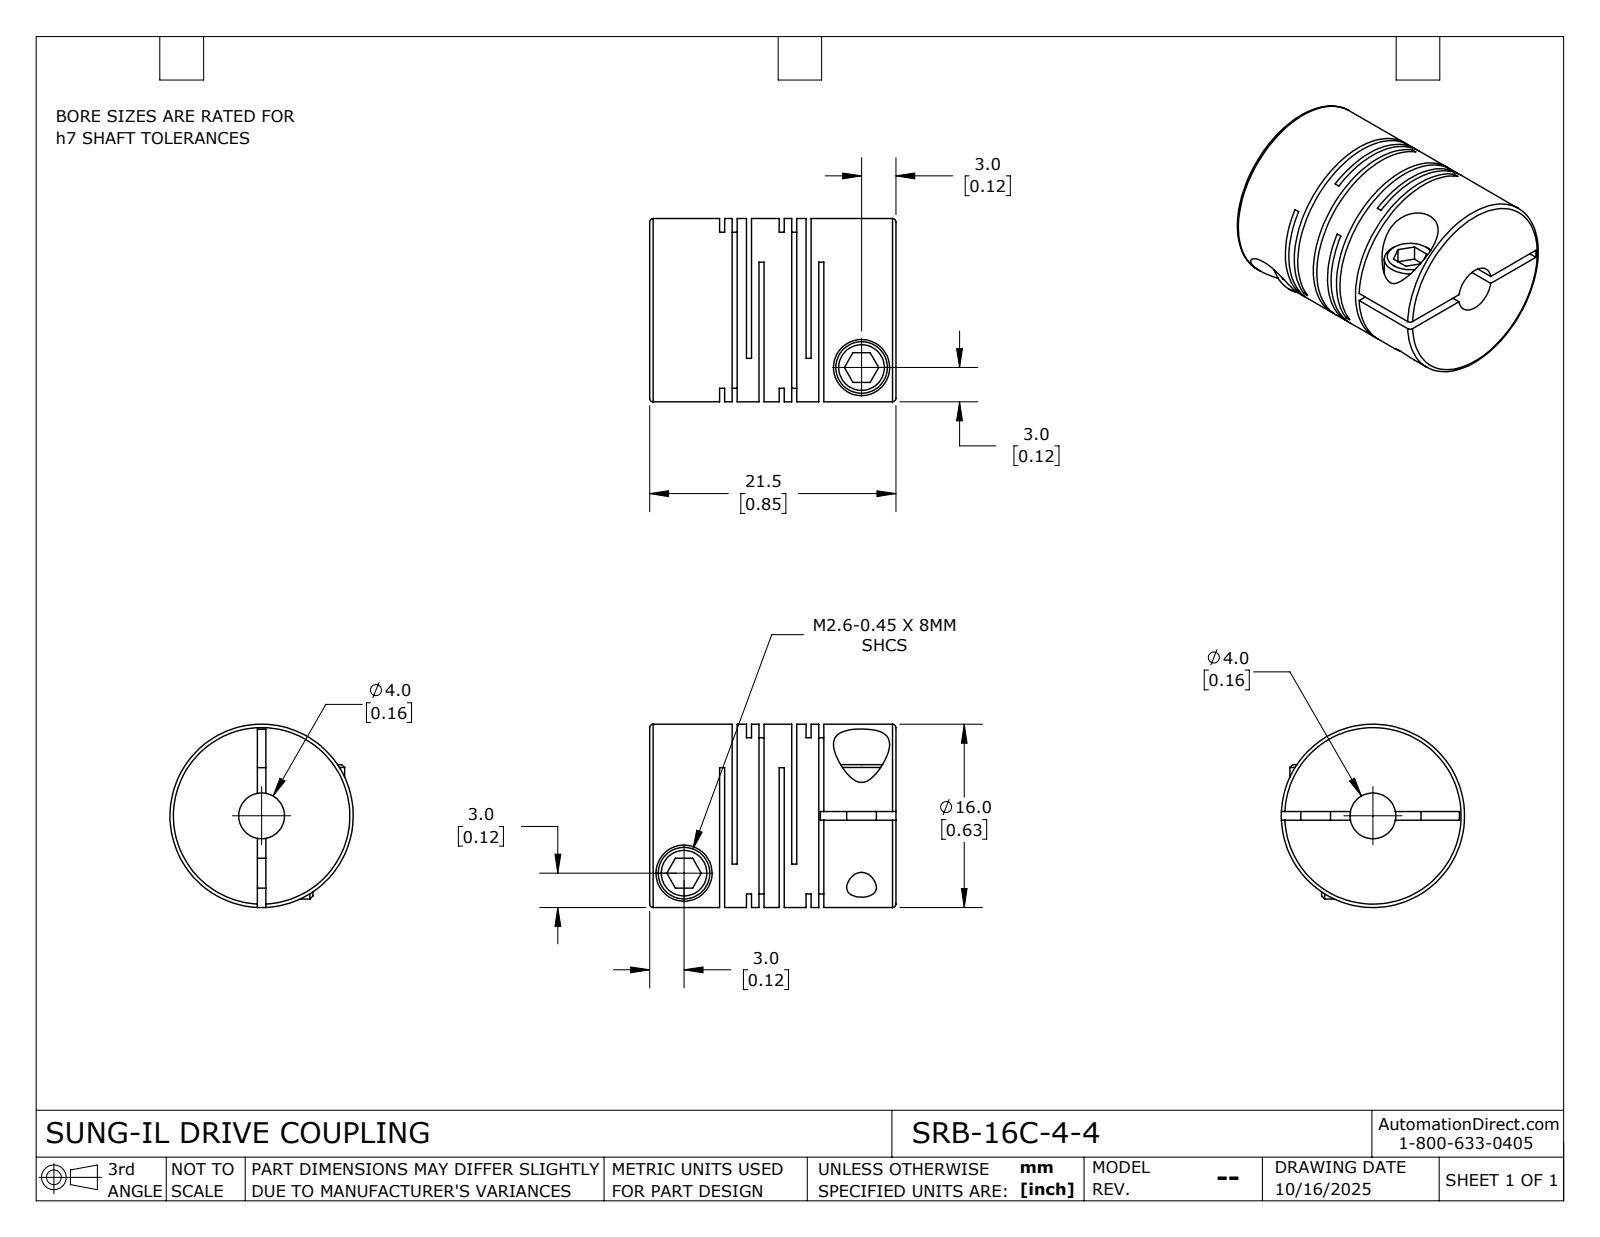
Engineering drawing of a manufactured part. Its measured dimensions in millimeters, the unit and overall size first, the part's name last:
Units: millimetres
Overall size (bounding box): 21.5 × 16 × 16
Round holes (diameter × count): ⌀2.6 ×2, ⌀4.9 ×2, ⌀4 ×1
Round bosses / shafts (diameter × count): ⌀4.5 ×2, ⌀16 ×1
Main face-to-face distances: 5.21, 0.44, 1.1, 2.35, 0.66, 1.91, 4.77, 1.25, 4.11, 2.86
Volume: 3 315 mm³ · Surface area: 4 457 mm²
Bodies: 1 solid, 115 faces (60 planar, 42 cylindrical, 13 other)
Part name (STEP PRODUCT): SRB-16C-4-4
STEP written by: SolidWorks 2024 (CONFIG_CONTROL_DESIGN)
